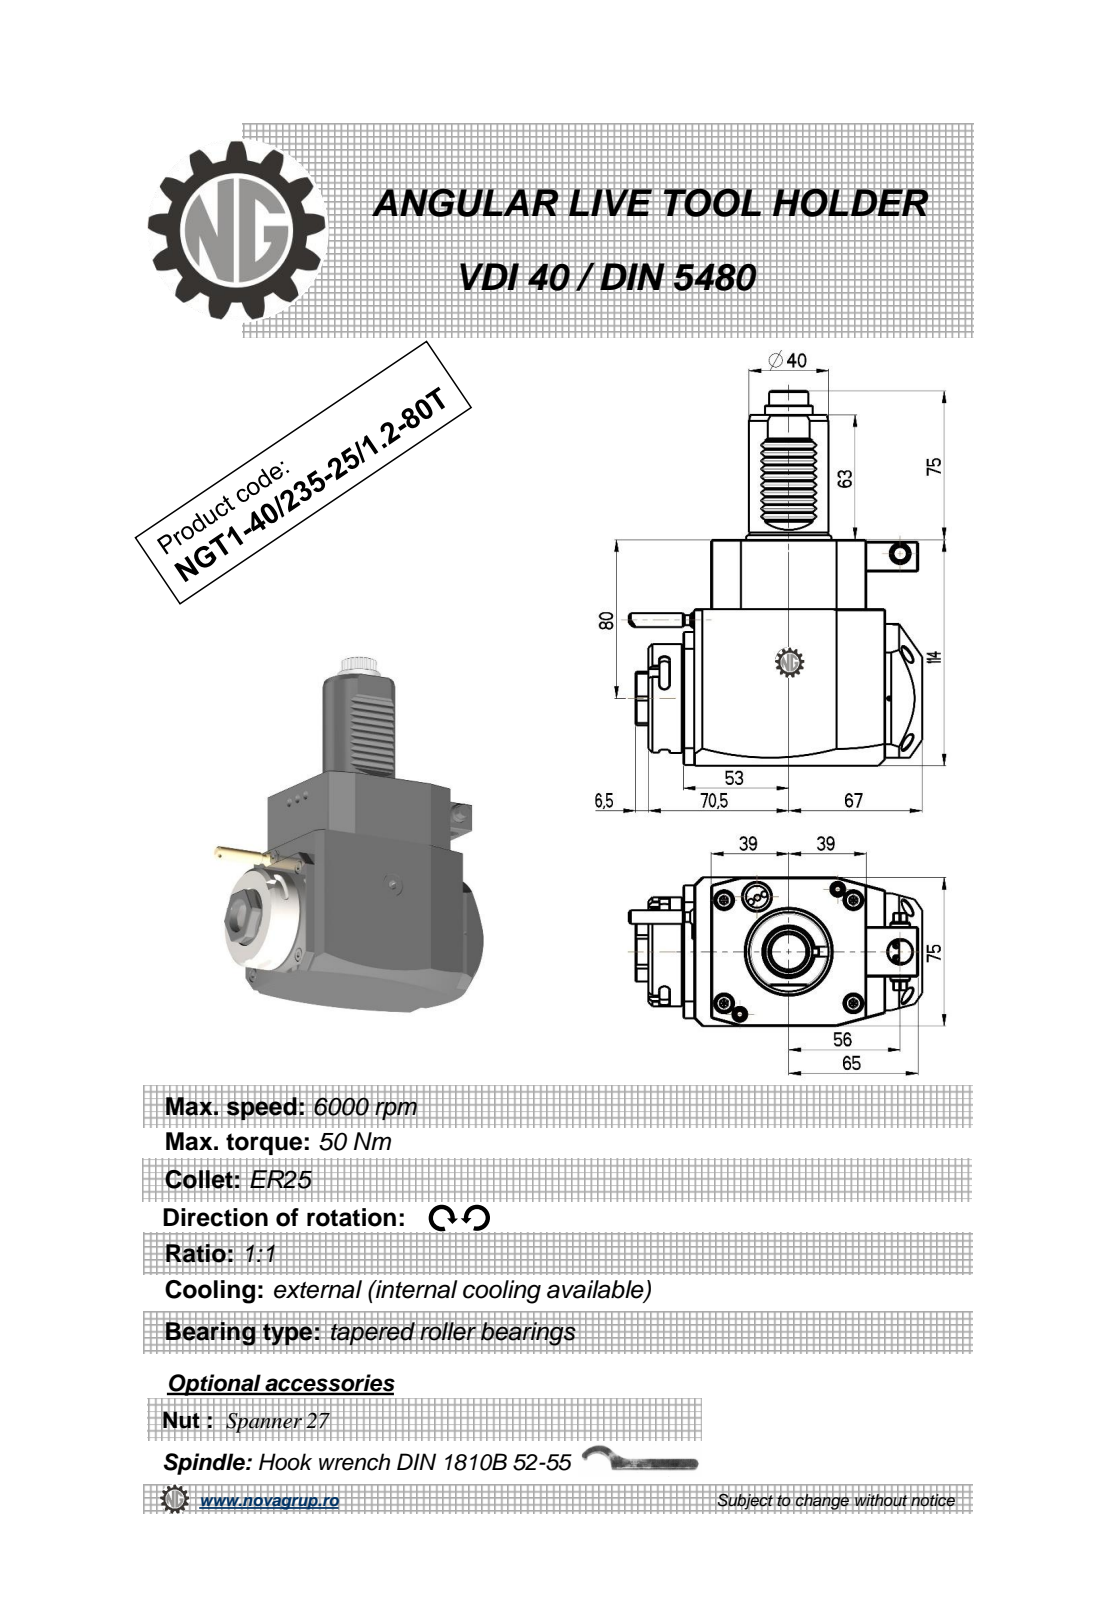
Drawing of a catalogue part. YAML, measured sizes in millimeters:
part_name: "NGT1_40_235_25_1_2_80T"
step_written_by: "PRO/ENGINEER BY PARAMETRIC TECHNOLOGY CORPORATION, 2010280 (CONFIG_CONTROL_DESIGN)"
units: millimeters
bodies: {solids: 1, faces: 458, planar: 186, cylindrical: 178, other: 94}
overall_size: [189, 147.33, 75]
volume: 959766
surface_area: 71151
round_holes:
  - {diameter: 2.5, count: 1}
  - {diameter: 3, count: 1}
  - {diameter: 9.5, count: 1}
  - {diameter: 12, count: 1}
  - {diameter: 18, count: 1}
round_bosses_or_shafts:
  - {diameter: 8, count: 2}
  - {diameter: 55, count: 1}
  - {diameter: 48, count: 1}
  - {diameter: 40, count: 1}
  - {diameter: 24, count: 1}
  - {diameter: 10, count: 1}
  - {diameter: 7, count: 1}
  - {diameter: 5, count: 1}
partial_cylinders:
  - {radius: 2.08, count: 48}
  - {radius: 0.3, count: 10}
  - {radius: 2.5, count: 6}
  - {radius: 15, count: 2}
  - {radius: 180, count: 2}
  - {radius: 3.85, count: 1}
  - {radius: 4.25, count: 1}
  - {radius: 9.08, count: 1}
face_to_face_distances: [75, 114, 14, 109.5, 92, 78, 17.5, 31.5, 79, 28]
hole_center_spacings: [36.47, 43.2, 71.5]
